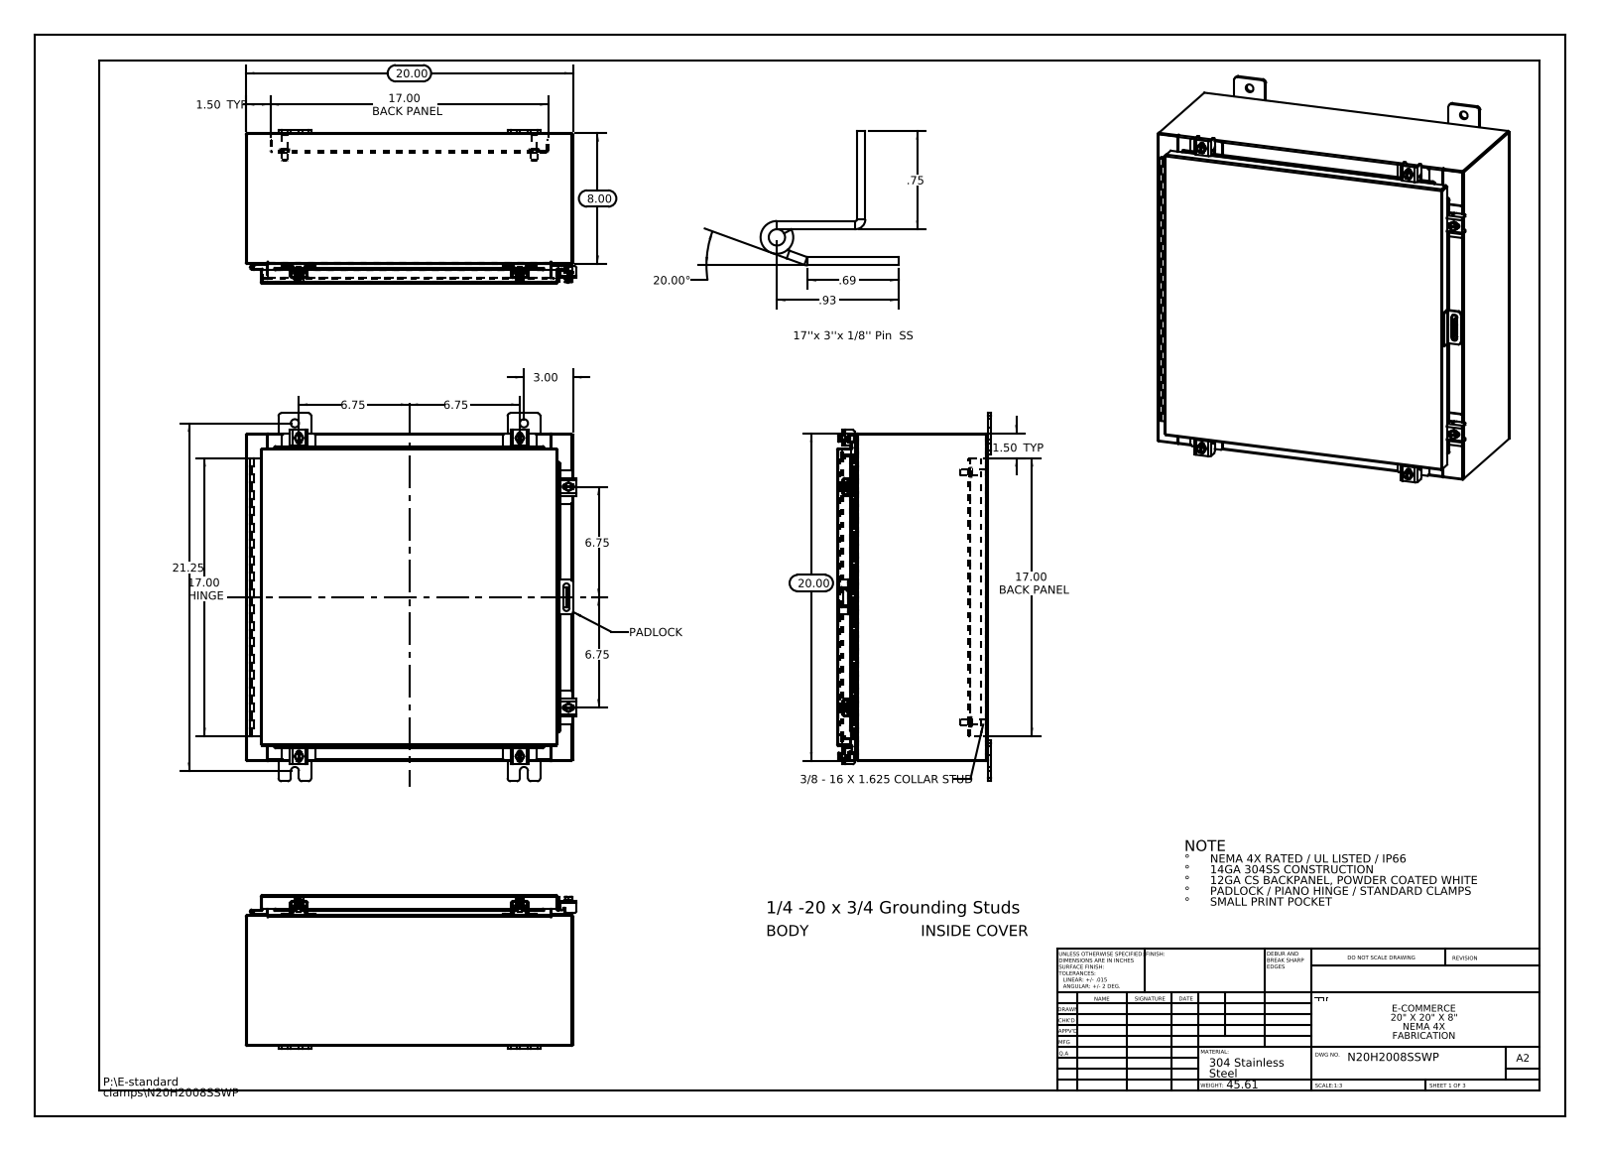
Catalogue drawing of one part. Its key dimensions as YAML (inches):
part_name: "N20H2008SSWP Cover; N20H2008SSWP Body; N20H2008SSWP Clamp Assembly; N20H2008SSWP Padlock Staple (+8 more)"
step_written_by: "SolidWorks 2013 (CONFIG_CONTROL_DESIGN)"
units: inches
bodies: {solids: 47, faces: 1613, planar: 860, cylindrical: 657, other: 96}
overall_size: [22.5, 20.211, 9.389]
volume: 160.7
surface_area: 4058
round_holes:
  - {diameter: 0.5, count: 8}
  - {diameter: 0.213, count: 6}
  - {diameter: 0.26, count: 6}
  - {diameter: 0.125, count: 2}
  - {diameter: 0.125, count: 1}
round_bosses_or_shafts:
  - {diameter: 0.25, count: 7}
  - {diameter: 0.5, count: 6}
  - {diameter: 0.399, count: 6}
  - {diameter: 0.625, count: 4}
  - {diameter: 0.375, count: 4}
  - {diameter: 0.33, count: 4}
partial_cylinders:
  - {radius: 0.06, count: 30}
  - {radius: 0.013, count: 25}
  - {radius: 0.19, count: 24}
  - {radius: 0.088, count: 21}
  - {radius: 0.12, count: 12}
  - {radius: 0.141, count: 12}
  - {radius: 0.125, count: 10}
  - {radius: 0.05, count: 9}
face_to_face_distances: [0.075, 9.126, 19.925, 9.201, 9.051, 19.85, 20, 0.104, 1, 1.075]
hole_center_spacings: [17.373, 14.528, 16.742, 22.532, 13.5, 0.431, 0.934, 1.858]
